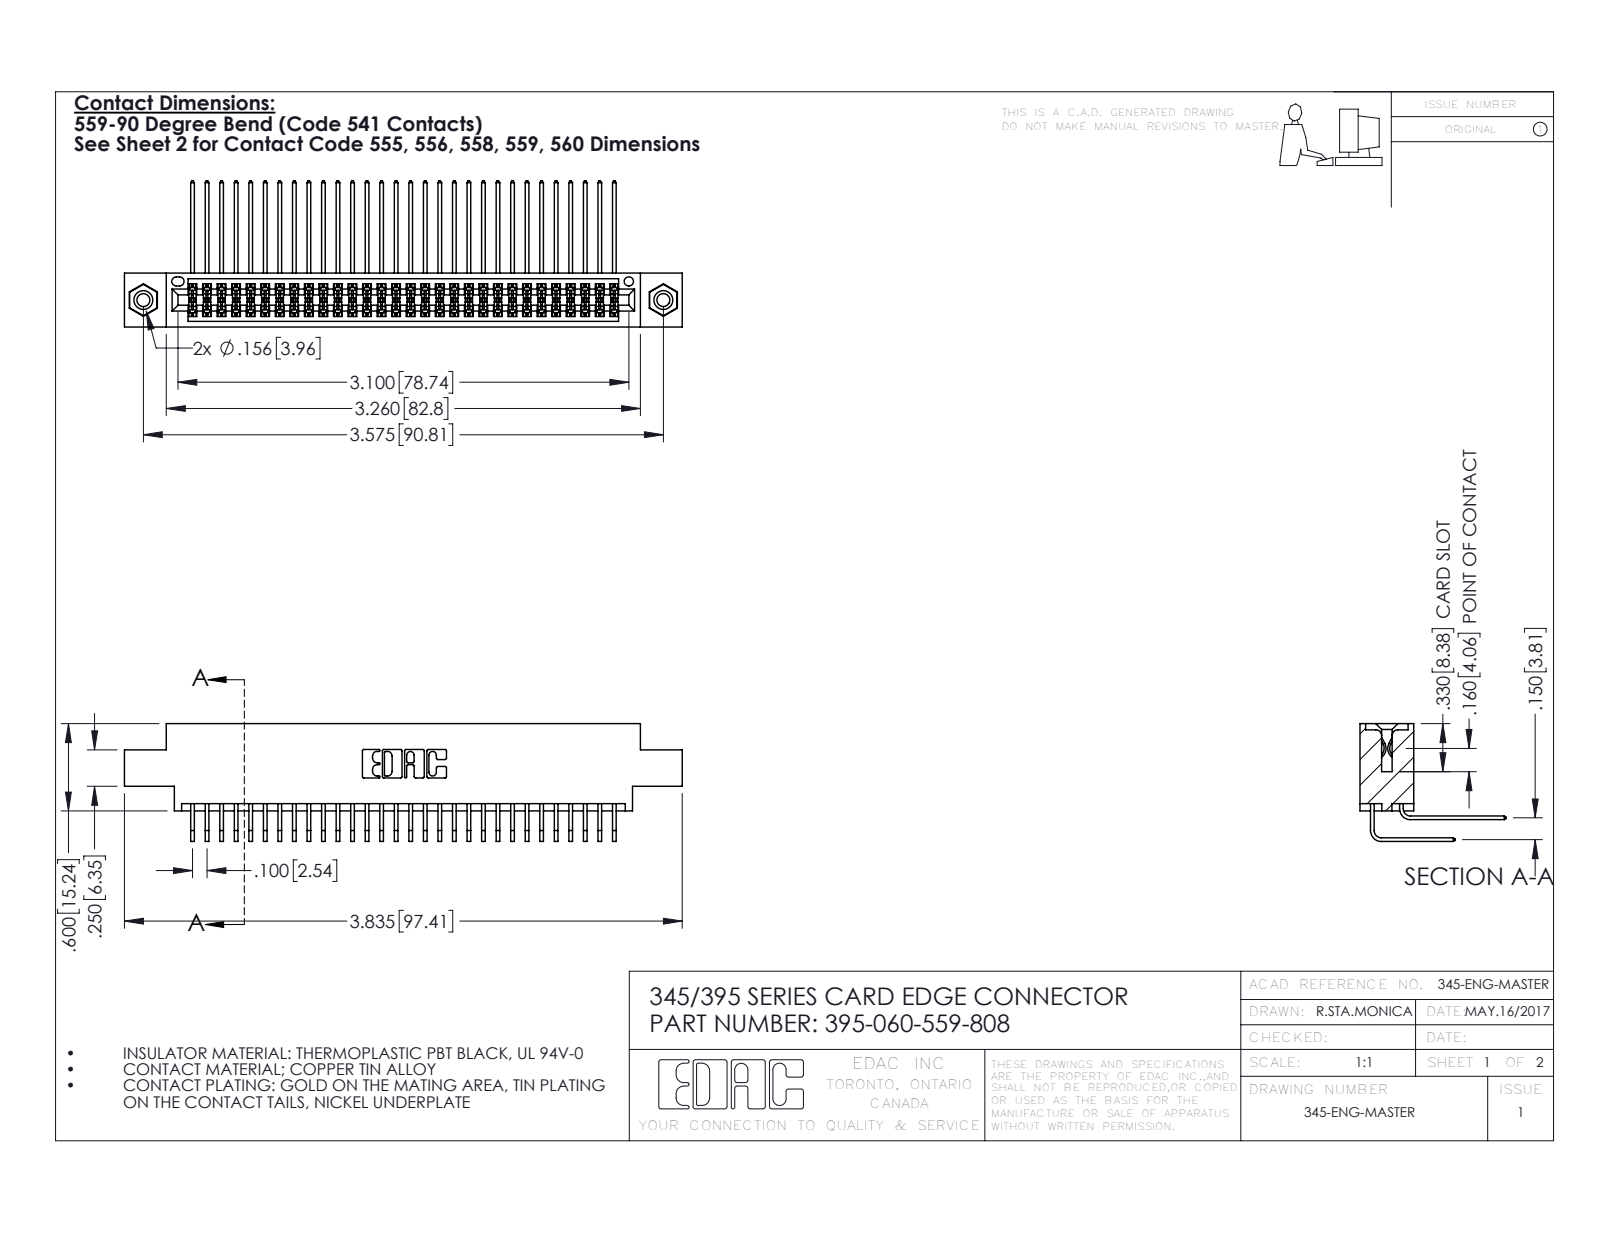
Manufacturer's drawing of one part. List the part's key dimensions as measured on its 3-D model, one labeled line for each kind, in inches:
Part name (STEP PRODUCT): 395-060-559-808; 345-292-001_558 559 Tail - 1; 345 Part_0.170 Offset - 0.156 Dia-TI; 345-250-001_345-250-003-102 (+1 more)
STEP written by: SolidWorks 2016 (CONFIG_CONTROL_DESIGN)
Units: inches
Bodies: 63 solids, 3310 faces (2216 planar, 1078 cylindrical, 16 other)
Overall size (bounding box): 3.835 × 1.005 × 0.809
Volume: 0.584 in³ · Surface area: 24.35 in²
Round holes (diameter × count): ⌀0.089 ×2, ⌀0.125 ×2, ⌀0.156 ×2, ⌀0.064 ×1
Round bosses / shafts (diameter × count): ⌀0.155 ×2
Partial cylindrical surfaces — rounded edges, fillets, slot ends (radius × count): R0.006 ×90, R0.01 ×22, R0.007 ×6, R0.031 ×6, R0.026 ×3, R0.014 ×2, R0.019 ×2, R0.022 ×2
Main face-to-face distances: 0.072, 0.298, 0.37, 0.2, 0.098, 0.272, 0.025, 0.225, 0.175, 0.15
Hole centre spacings: 0.27, 3.34, 3.575
